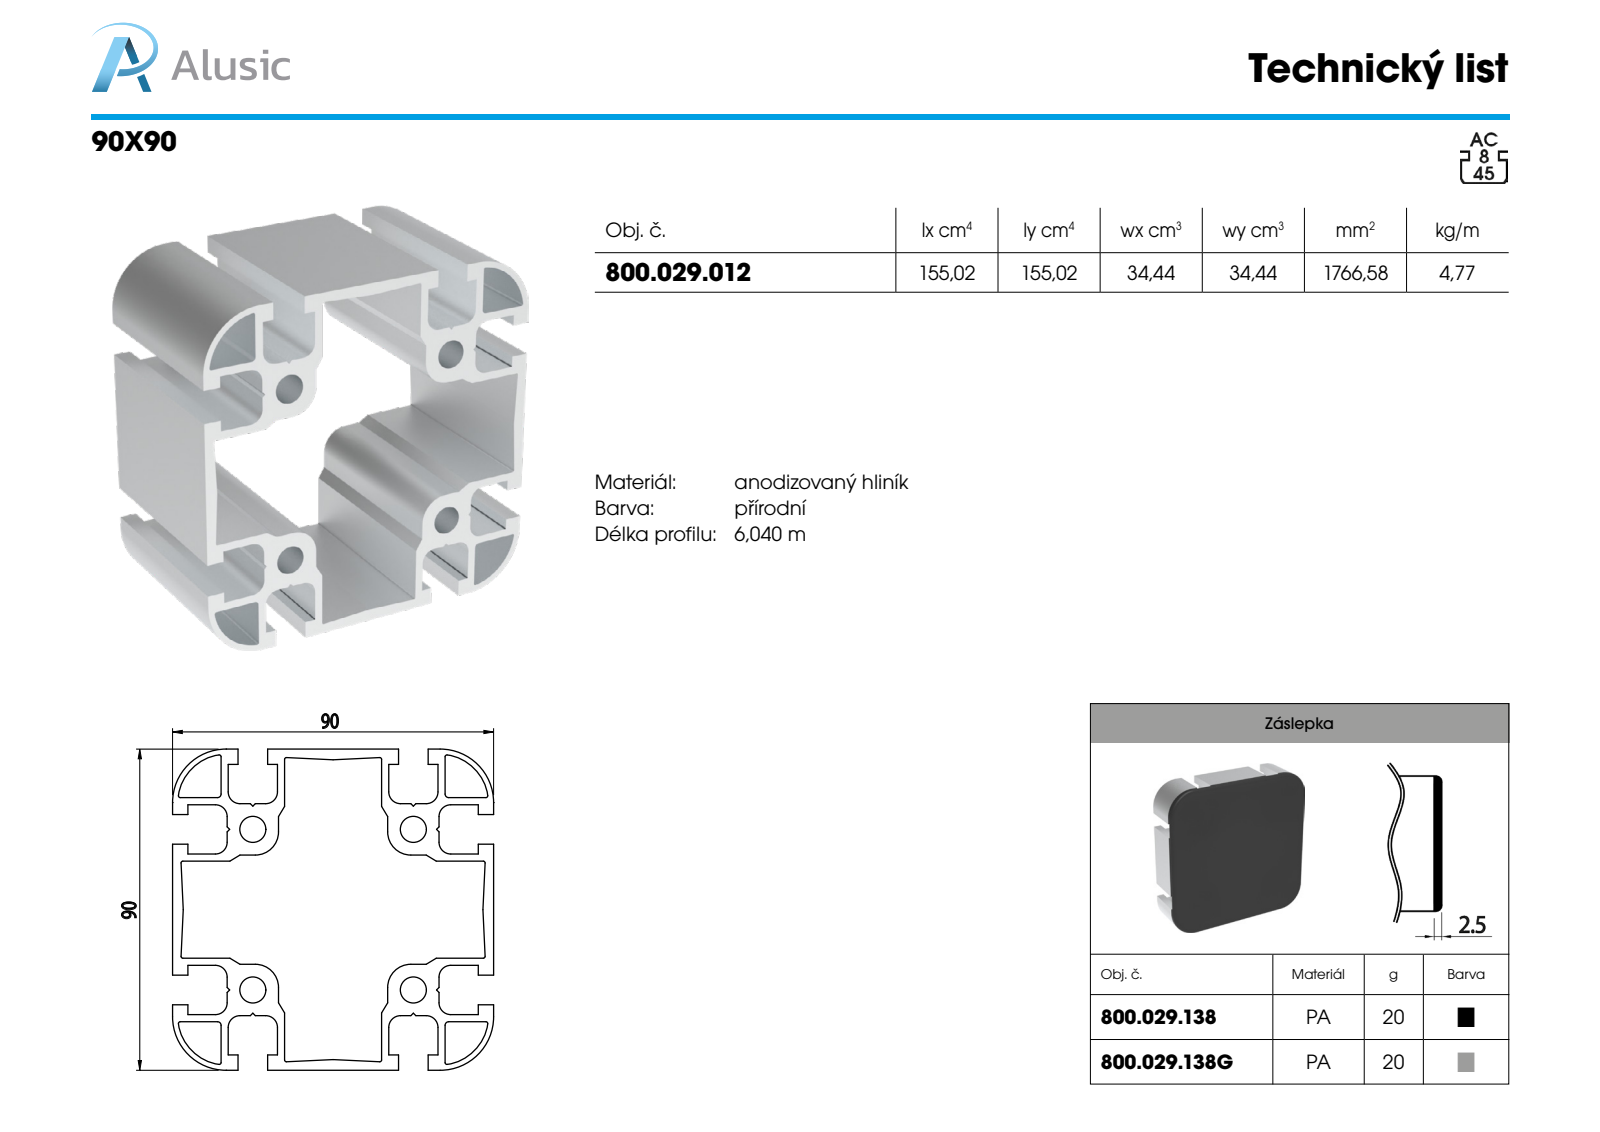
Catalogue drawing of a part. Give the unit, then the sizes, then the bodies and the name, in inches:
Units: inches
Overall size (bounding box): 3.937 × 3.544 × 3.544
Round holes (diameter × count): ⌀0.287 ×4
Partial cylindrical surfaces — rounded edges, fillets, slot ends (radius × count): R0.02 ×16, R0.13 ×16, R0.039 ×4, R0.256 ×4, R0.531 ×4, R0.591 ×4
Main face-to-face distances: 1.772, 1.772, 3.008, 0.634, 2.307, 1.237, 0.079, 0.701, 0.622, 0.067
Hole centre spacings: 1.772, 1.772, 2.506
Volume: 10.78 in³ · Surface area: 195.4 in²
Bodies: 1 solid, 194 faces (134 planar, 60 cylindrical, 0 other)
Part name (STEP PRODUCT): 800.029.012
STEP written by: SolidWorks 2018 (AUTOMOTIVE_DESIGN)
